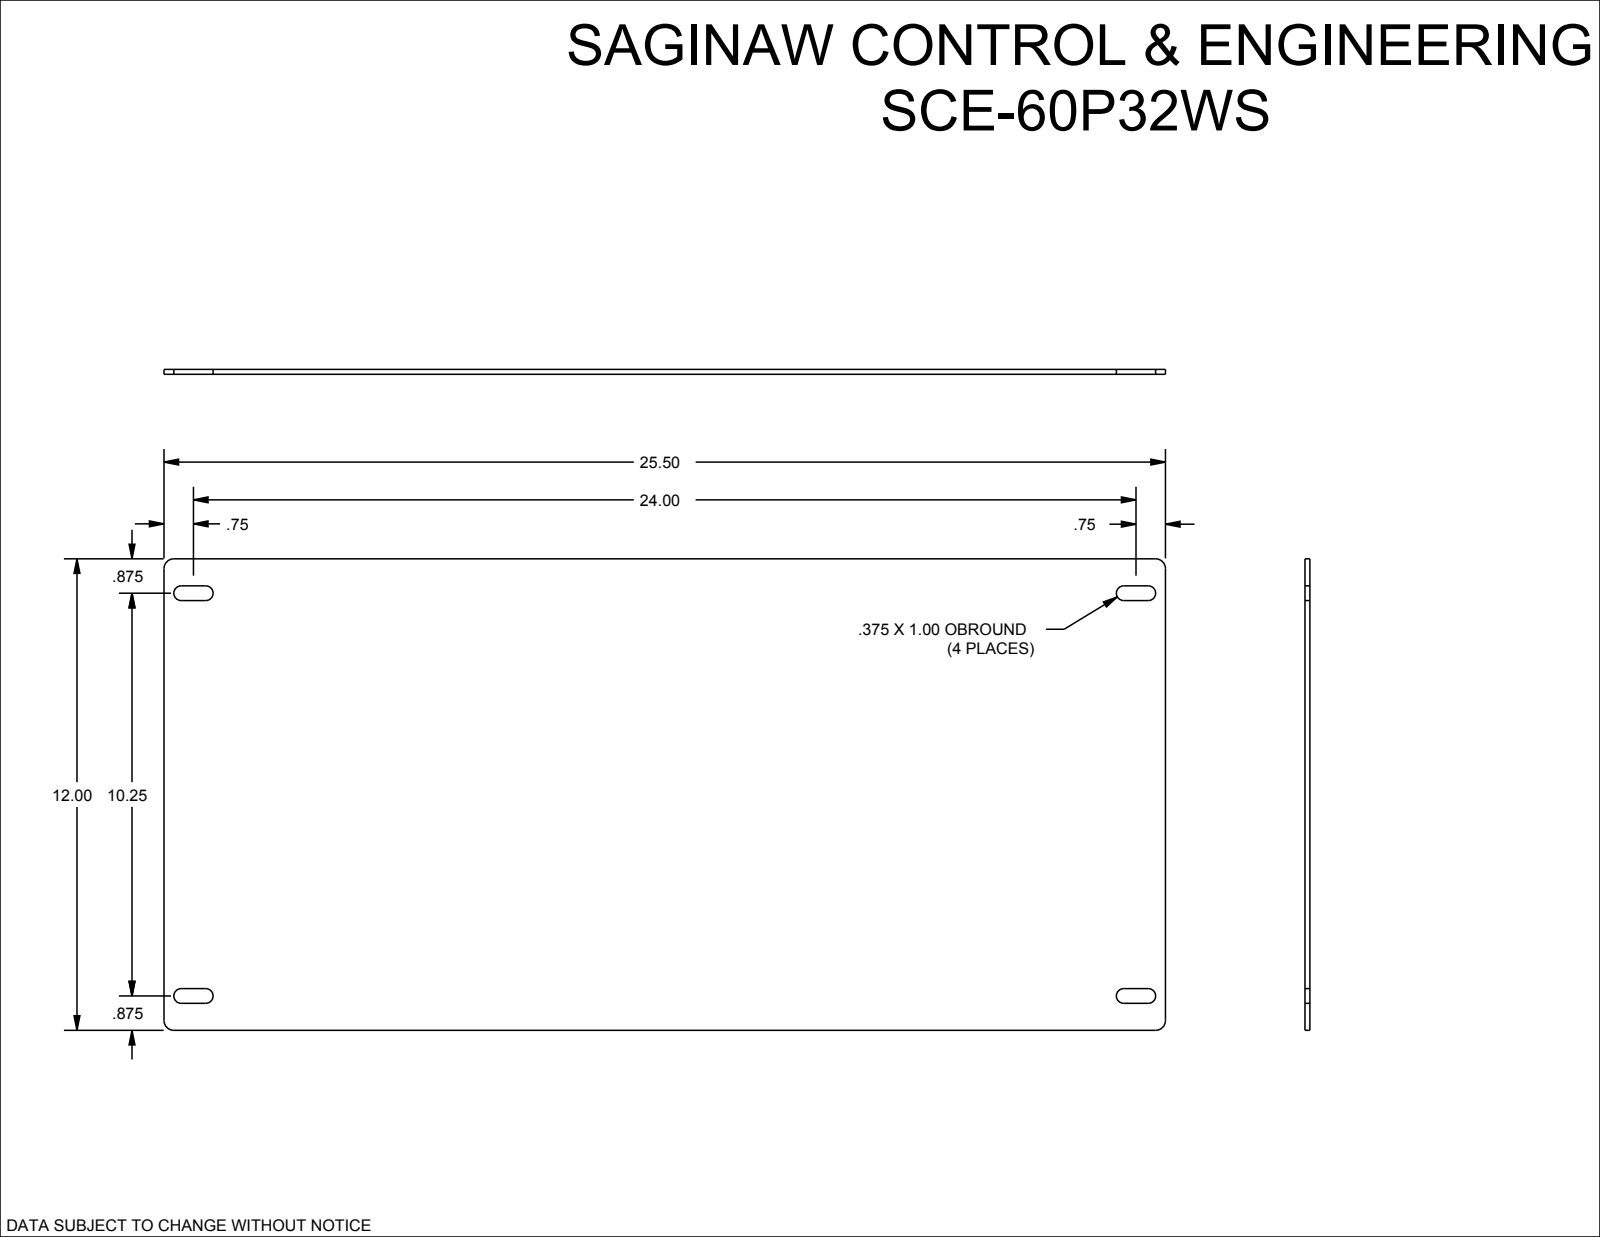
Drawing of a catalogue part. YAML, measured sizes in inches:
part_name: "SCE-60P32WS"
step_written_by: "SolidWorks 2019 (CONFIG_CONTROL_DESIGN)"
units: inches
bodies: {solids: 1, faces: 26, planar: 14, cylindrical: 12, other: 0}
overall_size: [25.5, 12, 0.125]
volume: 38.07
surface_area: 619.7
partial_cylinders:
  - {radius: 0.187, count: 4}
  - {radius: 0.188, count: 4}
  - {radius: 0.25, count: 4}
face_to_face_distances: [0.125, 12, 25.5, 0.687, 1.063, 10.937, 11.313, 0.375, 10.25, 10.625]
